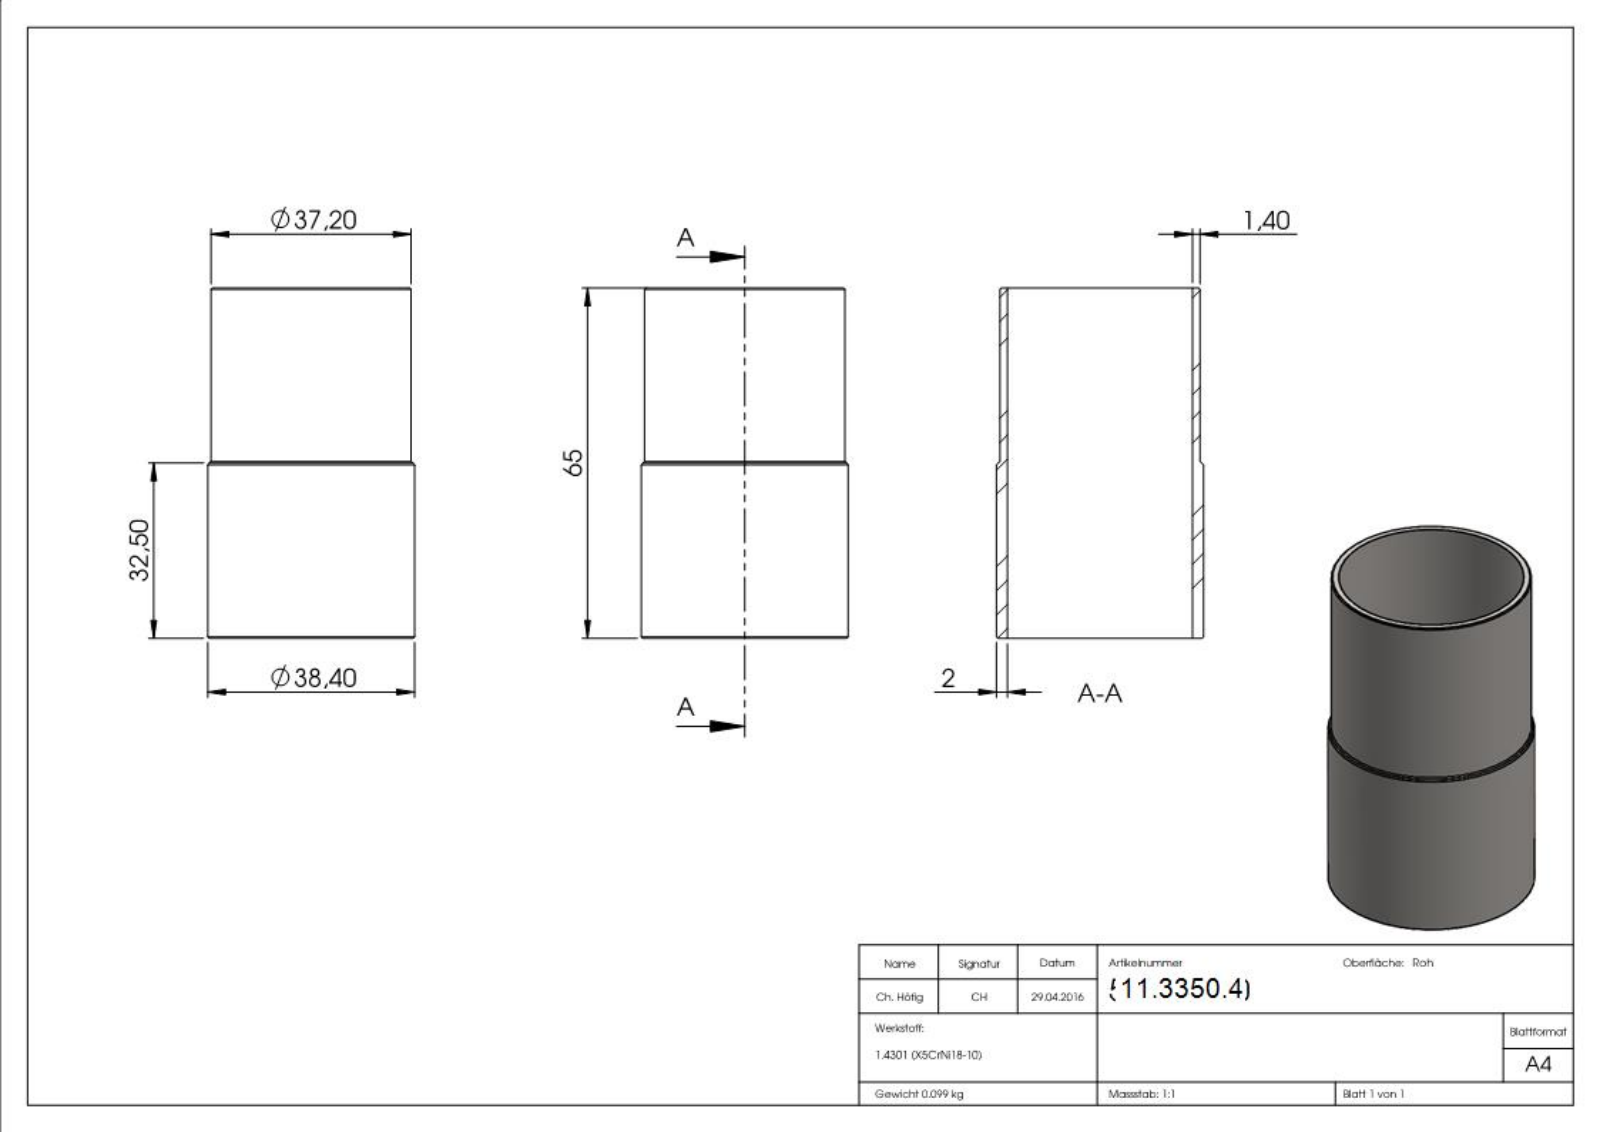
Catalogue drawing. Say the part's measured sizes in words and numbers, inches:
The part is named "50105-240". Its 3-D file was written by "SolidWorks 2015 (CONFIG_CONTROL_DESIGN)". It is 1 solid with 232 faces: 97 planar, 30 cylindrical and 105 other. Overall it measures 2.559 by 1.512 by 1.512 inches. Its volume is 0.765 cubic inches and its surface area 23.46 square inches. Round holes: 1 of diameter 1.354. Round bosses or shafts: 1 of diameter 1.512, 1 of diameter 1.465. Partial cylindrical surfaces (rounded edges, fillets, slot ends): 1 of radius 0.681. The main face-to-face distances are 2.559, 0.015, 0.052, 0.117, 0.462, 0.576, 0.333, 0.017, 0.035, 0.129.
